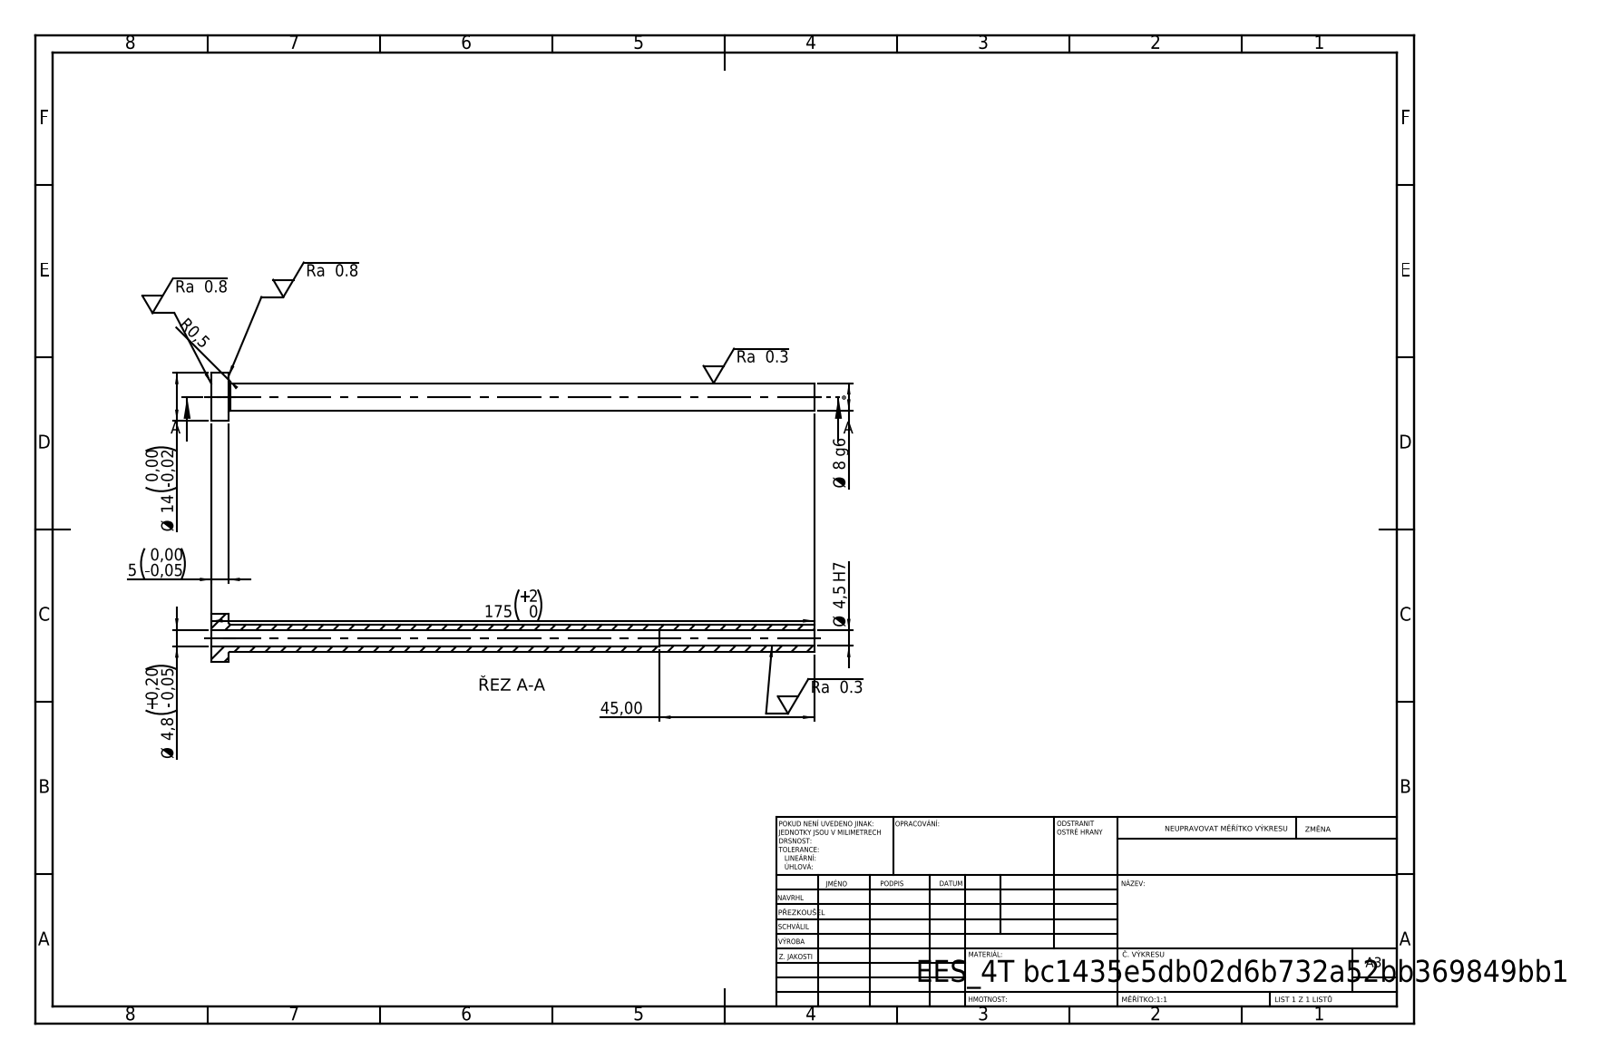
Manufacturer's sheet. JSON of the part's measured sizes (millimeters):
{"step_written_by": "SolidWorks 2019 (CONFIG_CONTROL_DESIGN)", "units": "millimeters", "bodies": {"solids": 1, "faces": 14, "planar": 4, "cylindrical": 8, "other": 2}, "overall_size": [175, 14, 14], "volume_mm3": 6248, "surface_area_mm2": 7360, "round_holes": [[4.5, 1], [4.8, 1]], "round_bosses_or_shafts": [[14, 1], [8, 1]], "face_to_face_distances": [5, 175, 170, 130, 125, 45]}
